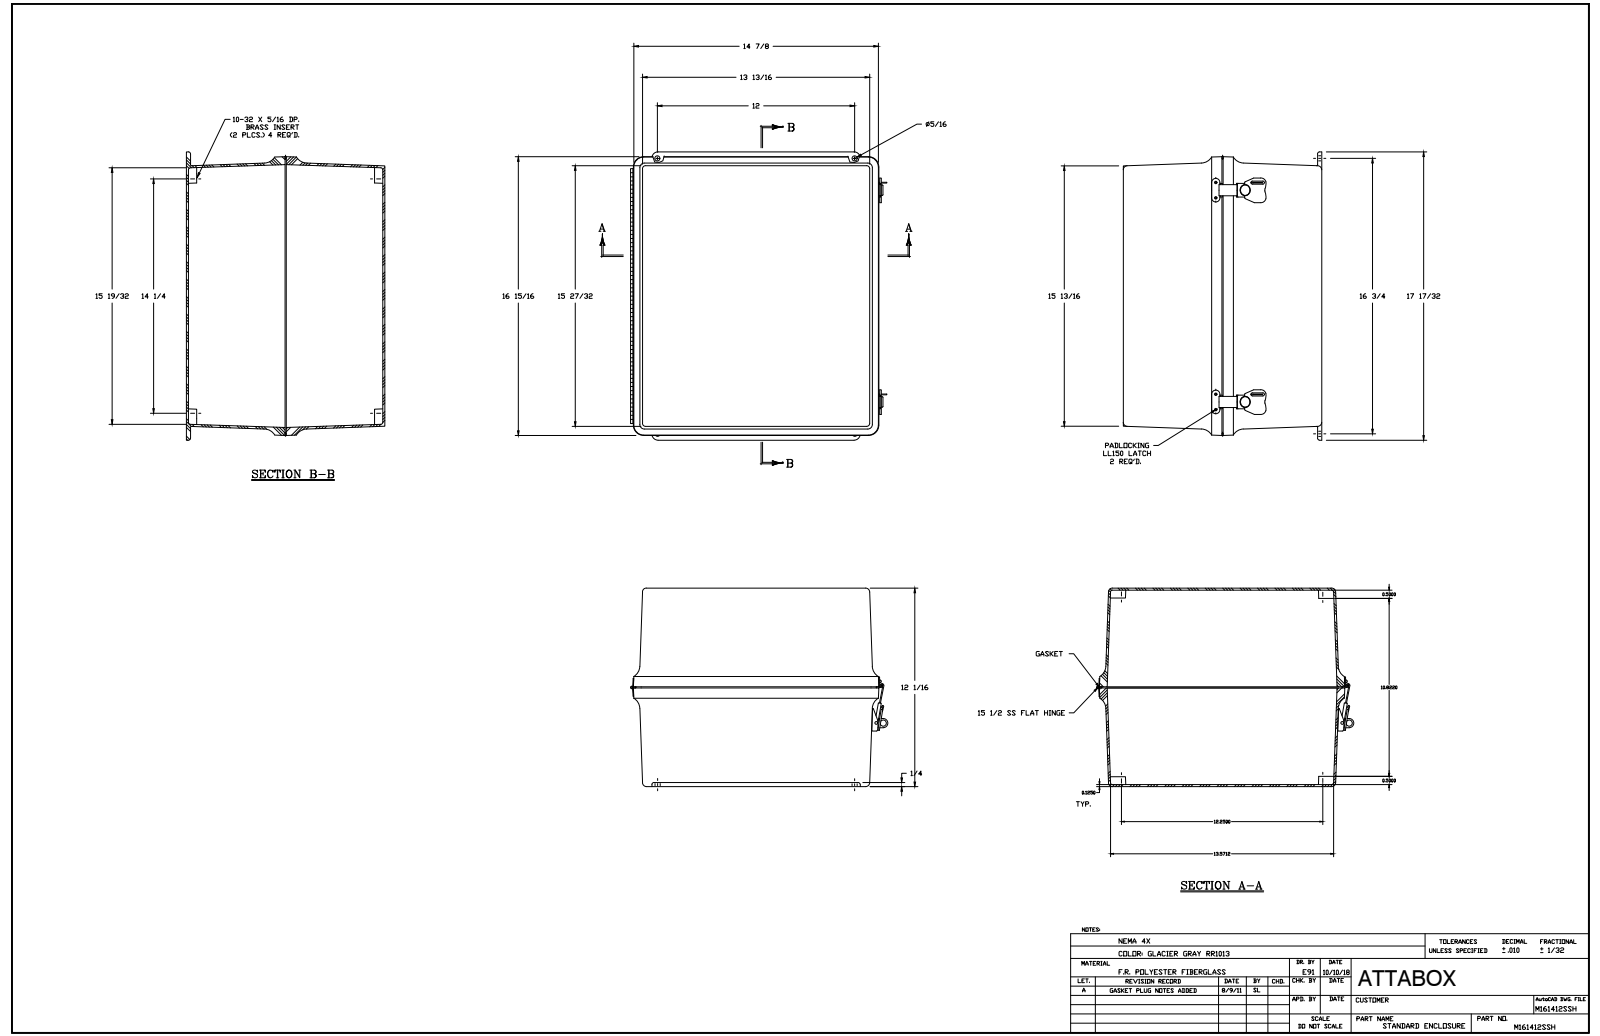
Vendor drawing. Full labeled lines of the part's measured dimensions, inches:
Part name (STEP PRODUCT): M161412SSH
STEP written by: SolidWorks 2018 (AUTOMOTIVE_DESIGN)
Units: inches
Bodies: 54 solids, 1499 faces (646 planar, 576 cylindrical, 277 other)
Overall size (bounding box): 17.531 × 15.595 × 12.055
Volume: 183.9 in³ · Surface area: 2 504 in²
Round holes (diameter × count): ⌀0.14 ×18, ⌀0.152 ×11, ⌀0.136 ×10, ⌀0.156 ×6, ⌀0.13 ×4, ⌀0.165 ×4, ⌀0.197 ×4, ⌀0.218 ×4, ⌀0.118 ×2, ⌀0.138 ×2, ⌀0.193 ×2, ⌀0.531 ×2
Round bosses / shafts (diameter × count): ⌀0.25 ×18, ⌀0.125 ×13, ⌀0.27 ×6, ⌀0.125 ×5, ⌀0.583 ×2, ⌀0.524 ×2, ⌀0.209 ×2, ⌀0.185 ×2
Partial cylindrical surfaces — rounded edges, fillets, slot ends (radius × count): R0.031 ×52, R0.079 ×19, R0.25 ×16, R0.75 ×14, R0.125 ×12, R0.039 ×8, R0.045 ×8, R0.047 ×8
Main face-to-face distances: 0.125, 11.93, 14.097, 0.125, 16.126, 12.055, 11.804, 13.972, 16.001, 14.222
Hole centre spacings: 3.75, 7.5, 1.321, 20.108, 12.868, 12.25, 13.22, 14.25
